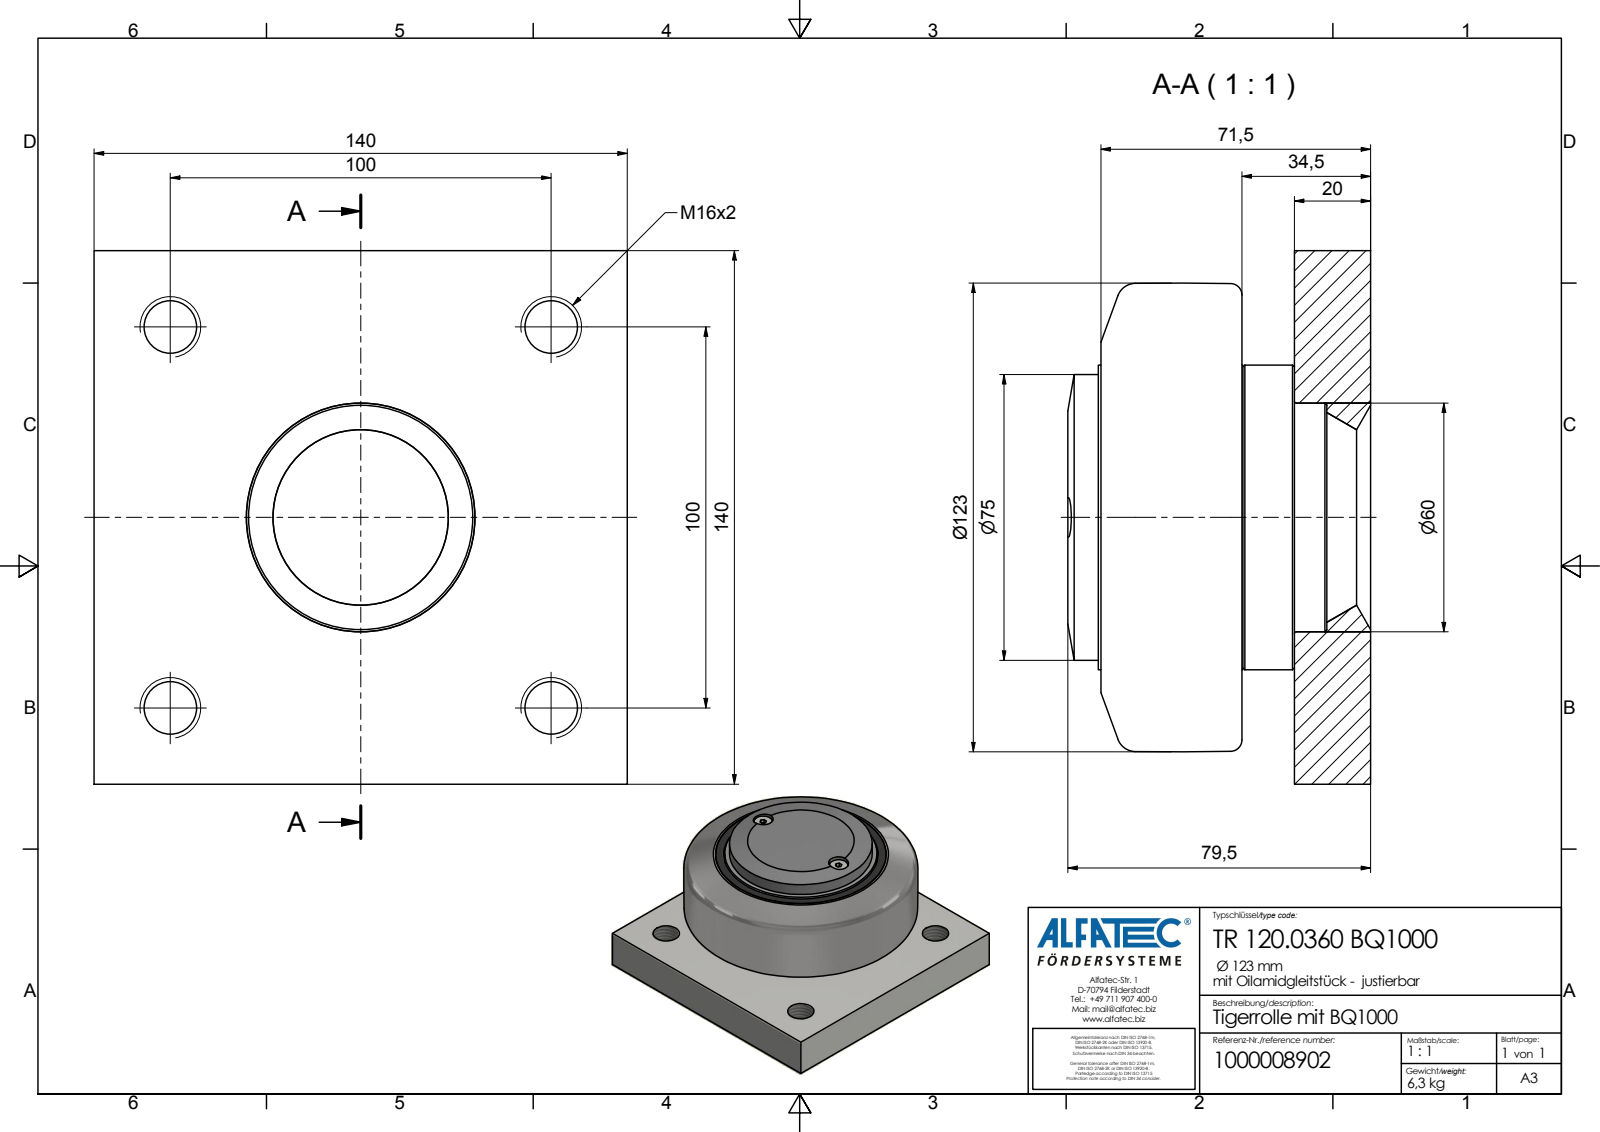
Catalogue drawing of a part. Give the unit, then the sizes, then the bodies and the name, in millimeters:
Units: millimetres
Overall size (bounding box): 140 × 140 × 79.5
Round holes (diameter × count): ⌀13.84 ×4, ⌀10.4 ×2, ⌀3 ×1, ⌀81 ×1, ⌀87 ×1, ⌀89.5 ×1, ⌀95 ×1
Round bosses / shafts (diameter × count): ⌀9.75 ×2, ⌀86.8 ×1, ⌀84.5 ×1, ⌀80 ×1, ⌀79 ×1, ⌀75 ×1
Partial cylindrical surfaces — rounded edges, fillets, slot ends (radius × count): R35.5 ×1
Main face-to-face distances: 20, 140, 33.8, 13.8, 79.5, 59.5, 45.7, 6.5, 30.5, 3.7
Hole centre spacings: 54.63, 70.71, 92.65, 100, 28, 141.42, 56
Volume: 840 114 mm³ · Surface area: 108 689 mm²
Bodies: 2 solids, 71 faces (36 planar, 24 cylindrical, 11 other)
Part name (STEP PRODUCT): TR 120.0360 BQ1000_Kontur
STEP written by: Autodesk Inventor 2020 (CONFIG_CONTROL_DESIGN)
